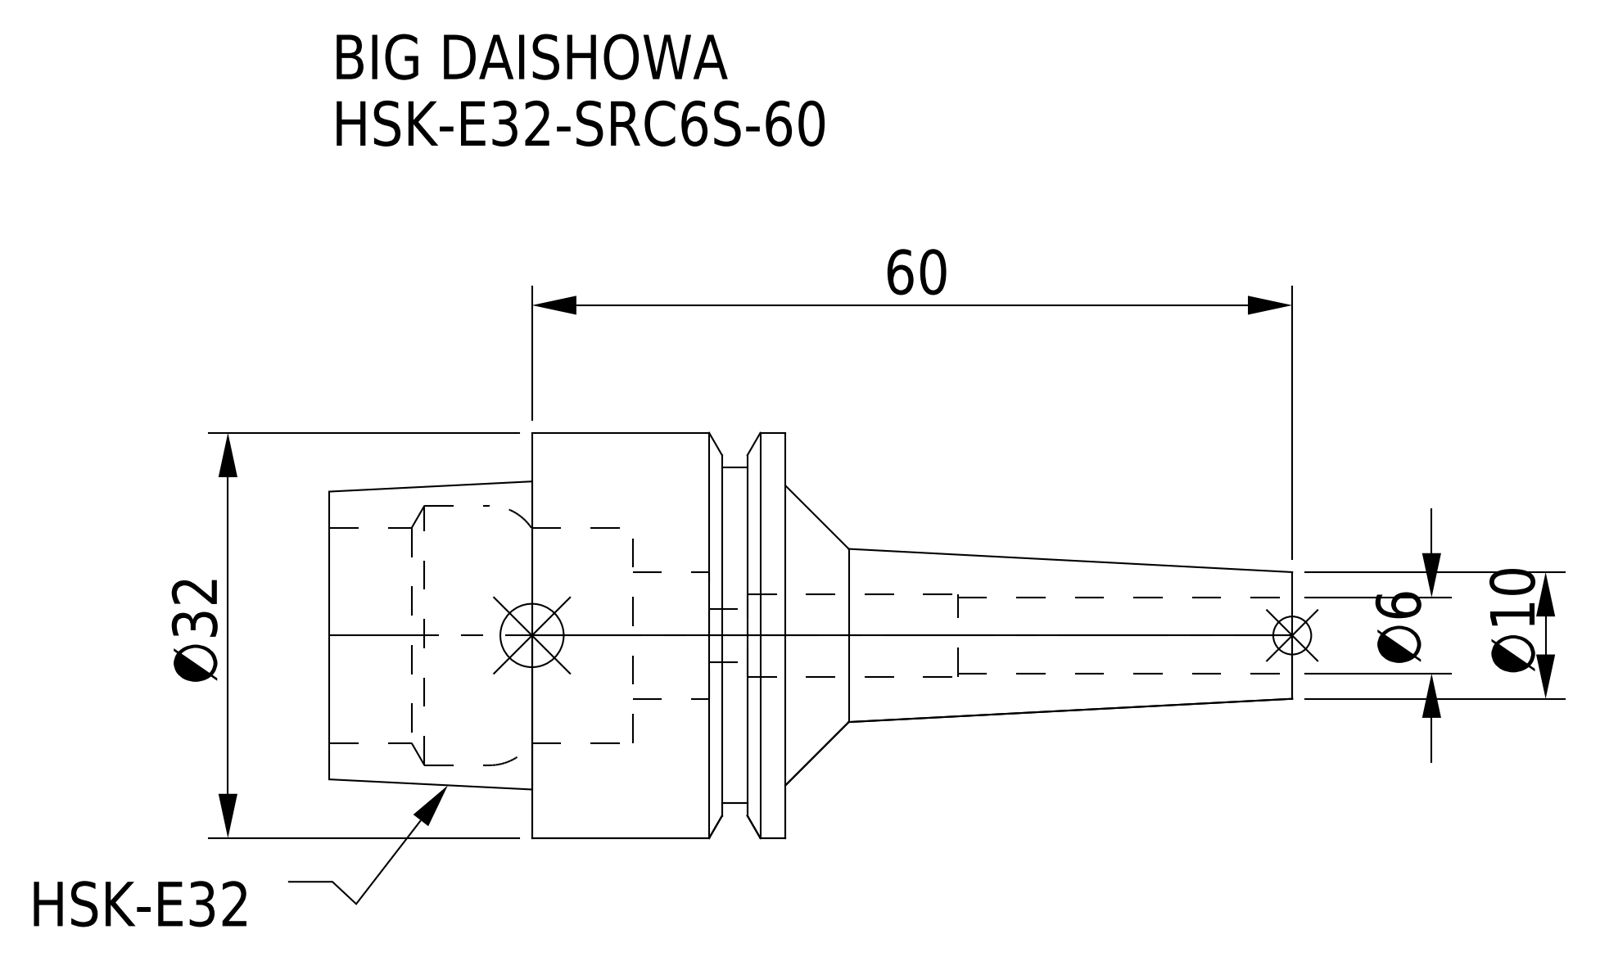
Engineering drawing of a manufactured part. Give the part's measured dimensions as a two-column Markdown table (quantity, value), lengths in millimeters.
| quantity | value |
| --- | --- |
| part name | HSK-E32-SRC6S-60 |
| STEP written by | CREO PARAMETRIC BY PTC INC, 2016380 (AUTOMOTIVE_DESIGN) |
| units | millimeters |
| bodies | 1 solid, 46 faces (10 planar, 22 cylindrical, 14 other) |
| overall size | 76 × 32 × 32 |
| volume | 19 579 mm³ |
| surface area | 8 925 mm² |
| round holes (diameter × count) | 4.2 × 1, 6 × 1, 6.5 × 1, 10 × 1, 17 × 1, 20.5 × 1 |
| round bosses / shafts (diameter × count) | 32 × 1, 26.5 × 1 |
| main face-to-face distances | 20, 36, 16, 12.05, 7.95, 23.95, 3, 9.05, 17, 33 |
